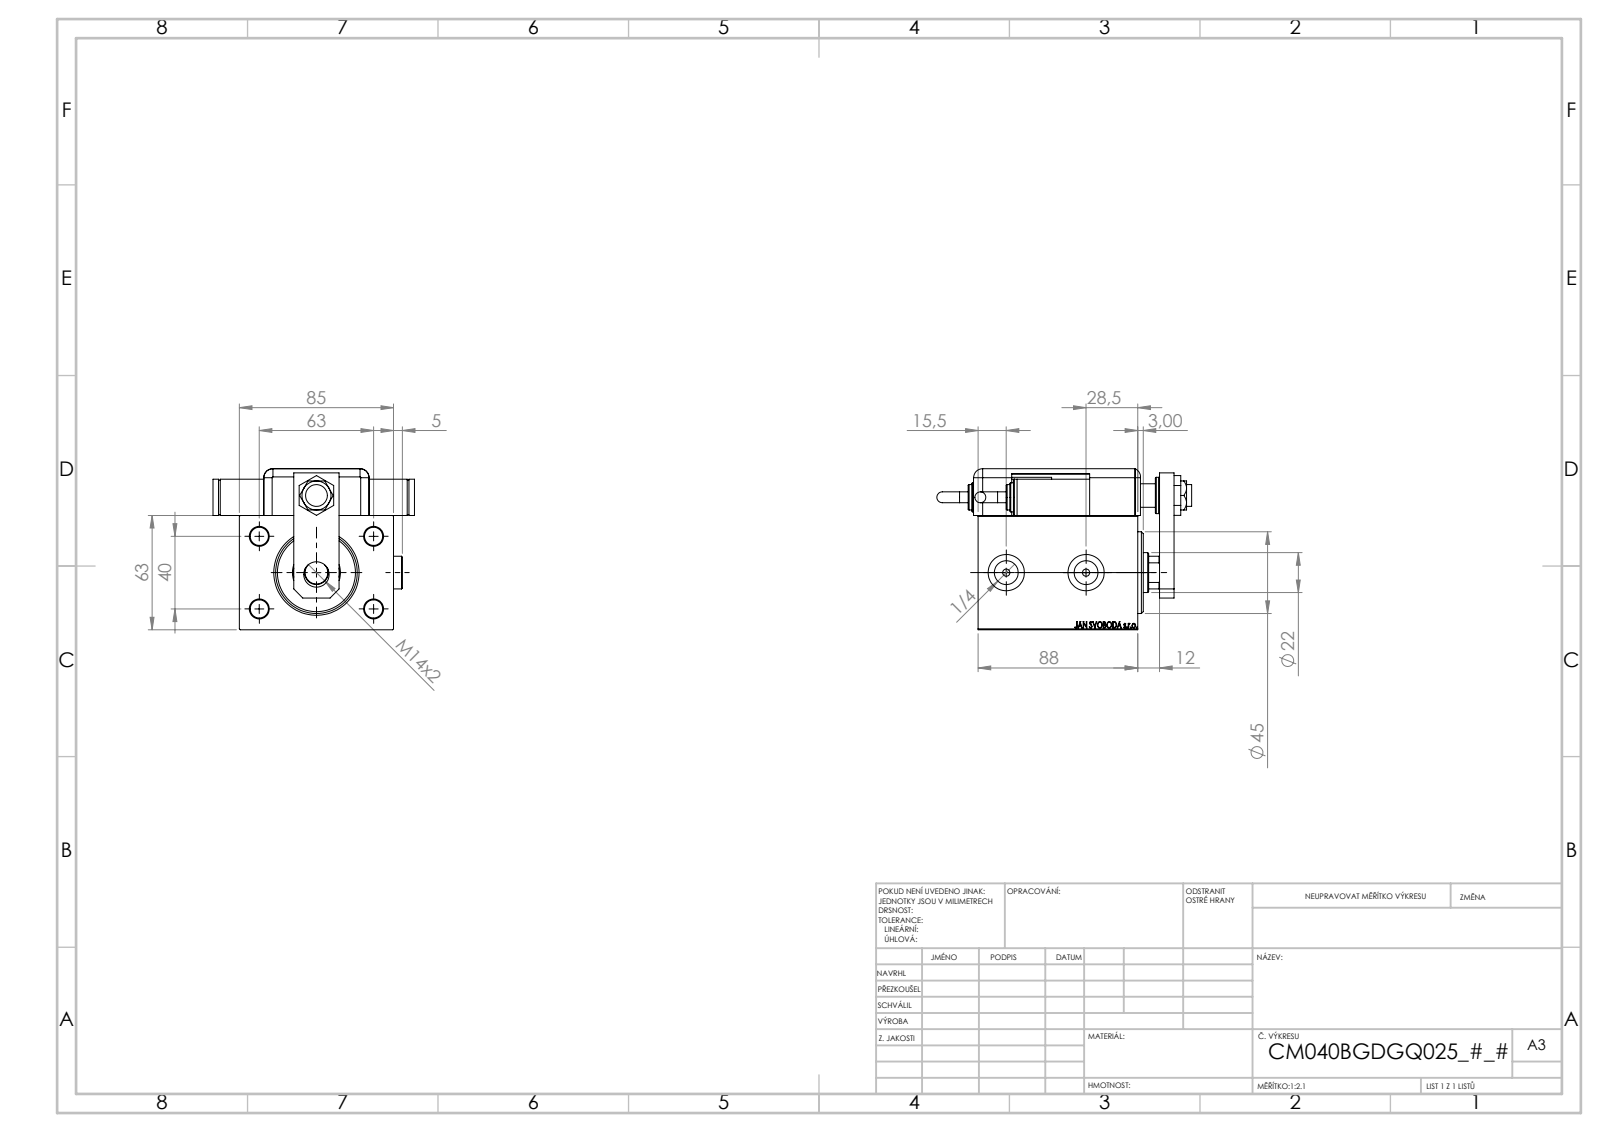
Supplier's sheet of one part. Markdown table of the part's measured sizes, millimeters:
| quantity | value |
| --- | --- |
| part name | MAGNETIC SWITCH Q; V450CM_B_Body; V450CM_VC_B; SWITCH Q (+7 more) |
| STEP written by | SolidWorks 2019 (CONFIG_CONTROL_DESIGN) |
| units | millimeters |
| bodies | 15 solids, 1319 faces (641 planar, 125 cylindrical, 553 other) |
| overall size | 140.46 × 111 × 88.8 |
| volume | 569 247 mm³ |
| surface area | 123 212 mm² |
| round holes (diameter × count) | 4 × 4, 10 × 4, 8 × 2, 13.16 × 2, 14 × 2, 20 × 2, 12 × 1, 12.5 × 1, 13 × 1, 22 × 1, 25.5 × 1, 26.5 × 1 |
| round bosses / shafts (diameter × count) | 20 × 3, 18 × 2, 16 × 2, 14 × 2, 6 × 2 |
| partial cylindrical surfaces (radius × count) | 5 × 9, 10 × 1, 10.5 × 1 |
| main face-to-face distances | 3, 63, 13.5, 85, 12, 88, 83, 20, 88.8, 1.5 |
| hole center spacings | 37.31, 36.79, 37.86, 38.71, 40, 63, 69.99, 74.63 |
